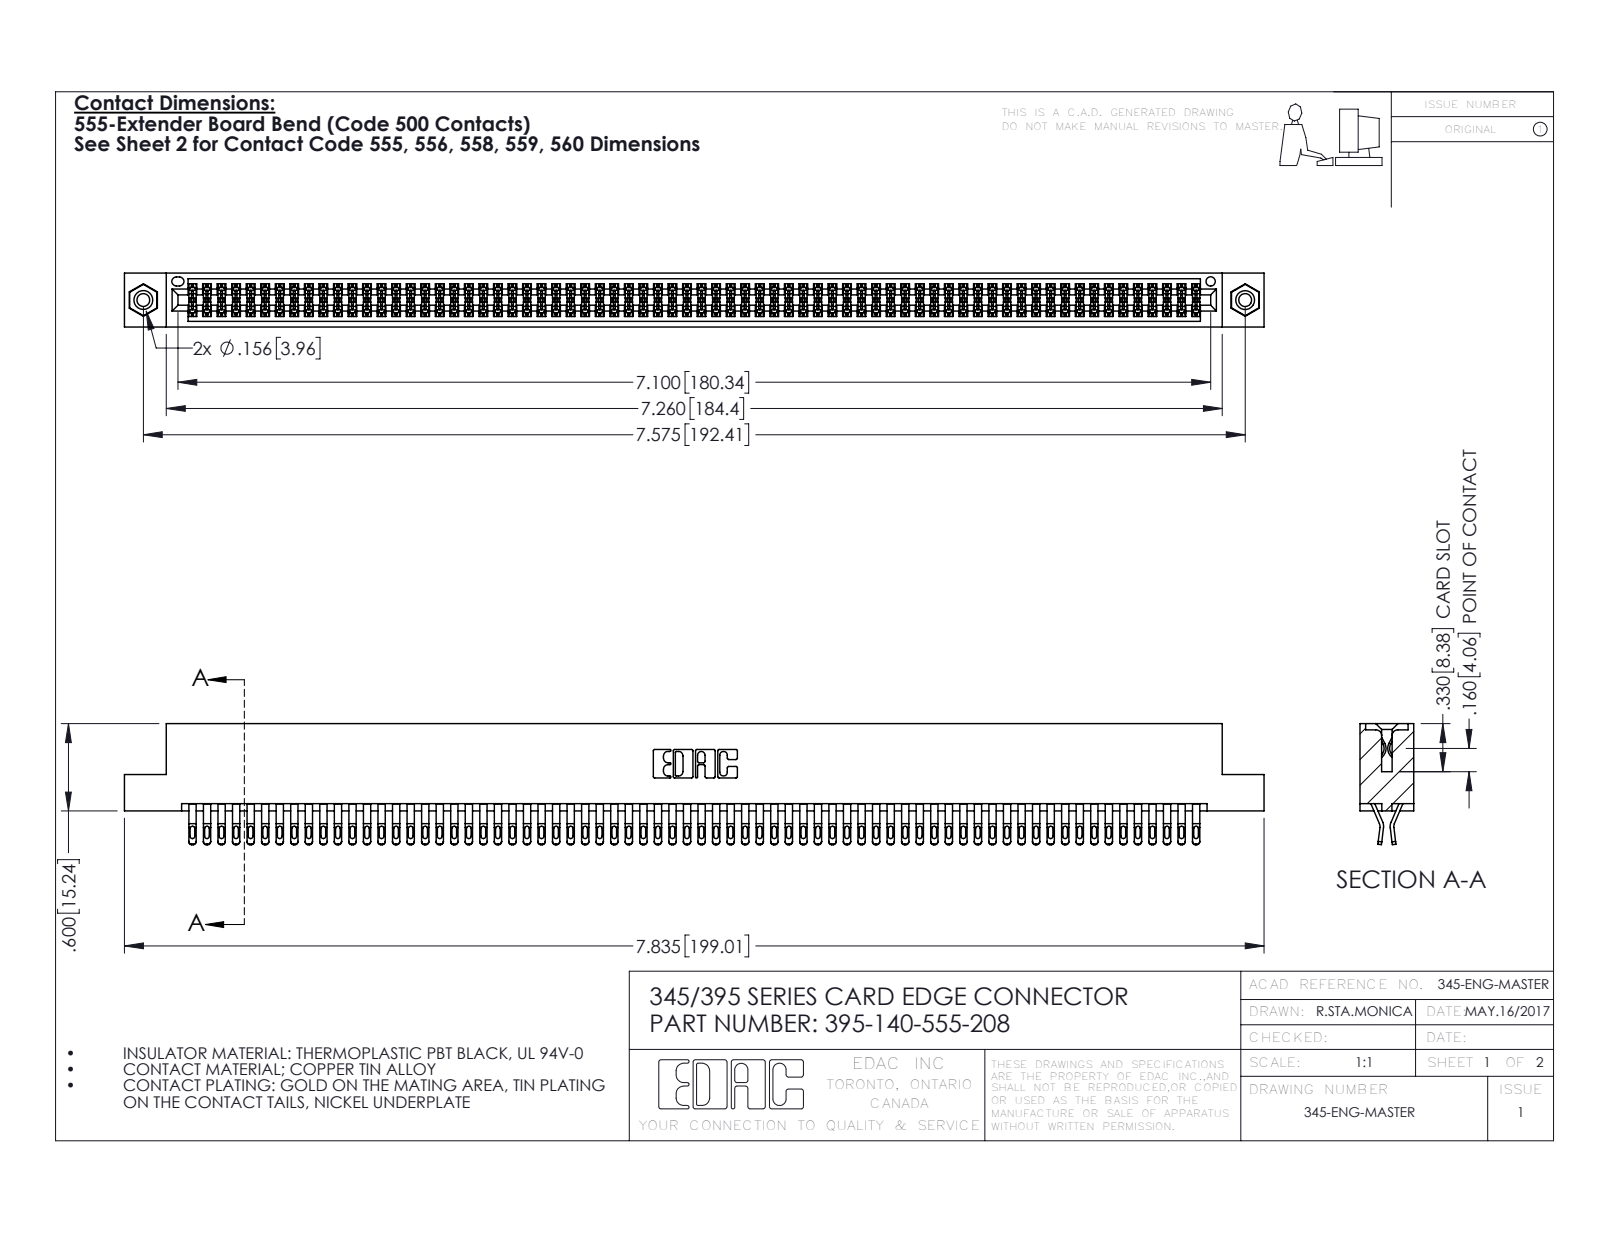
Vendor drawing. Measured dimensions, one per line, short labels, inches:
name: 395-140-555-208; 345-292-001_555 Tail; 345-250-001_345-250-003-102; 345 Part_Flush Mounting Lugs - 0.156 Dia-TI
written by: SolidWorks 2016 (CONFIG_CONTROL_DESIGN)
unit: in
bodies: 143 solids, 8026 faces (4452 planar, 3558 cylindrical, 16 other)
size: 7.835 × 0.832 × 0.37
volume: 1.22 in³; area: 48.85 in²
holes: 2× ⌀0.089, 2× ⌀0.125, 2× ⌀0.156, 1× ⌀0.064
bosses: 2× ⌀0.155
rounds: 350× R0.016, 280× R0.02, 210× R0.006, 22× R0.01, 6× R0.007, 6× R0.031, 3× R0.026, 2× R0.01
face distances: 0.072, 0.298, 0.025, 0.37, 0.2, 0.098, 0.272, 0.225, 0.175, 0.149
hole spacings: 0.27, 7.339, 7.575
